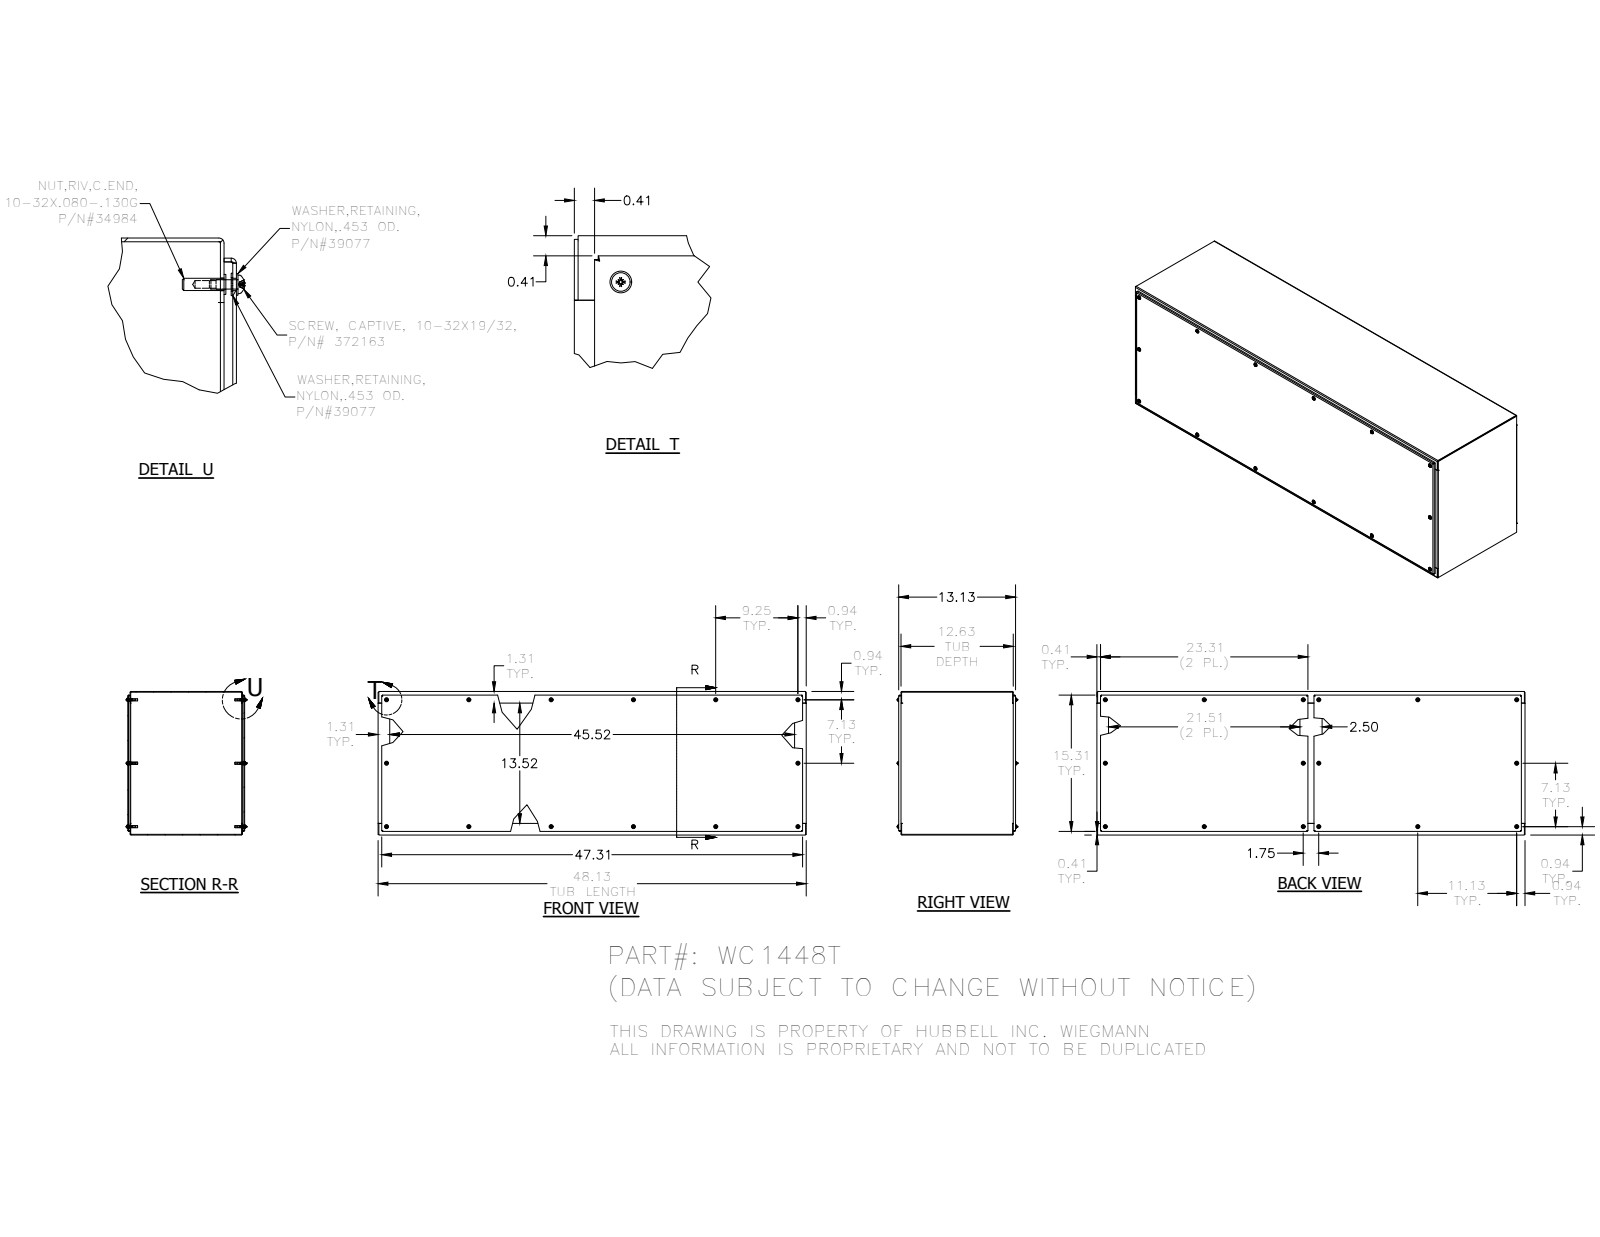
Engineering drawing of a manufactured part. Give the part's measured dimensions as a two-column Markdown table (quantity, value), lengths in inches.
| quantity | value |
| --- | --- |
| part name | 34984; WC14TLRS; WC1448TTB; 39035 (+6 more) |
| STEP written by | Autodesk Inventor 2016 (AUTOMOTIVE_DESIGN) |
| units | inches |
| bodies | 136 solids, 2638 faces (1378 planar, 550 cylindrical, 710 other) |
| overall size | 48.125 × 16.125 × 13.451 |
| volume | 255.1 in³ |
| surface area | 6 977 in² |
| round holes (diameter × count) | 0.25 × 27, 0.156 × 26, 0.196 × 26, 0.188 × 24, 0.278 × 24, 0.257 × 22, 0.179 × 4 |
| round bosses / shafts (diameter × count) | 0.406 × 26, 0.248 × 26, 0.453 × 24, 0.437 × 24, 0.373 × 24, 0.19 × 24 |
| partial cylindrical surfaces (radius × count) | 0.089 × 20, 0.031 × 18, 0.105 × 18 |
| main face-to-face distances | 0.074, 13.051, 16.051, 12.977, 13.125, 12.801, 0.25, 15.977, 16.125, 48.051 |
| hole center spacings | 14.25, 9.25, 16.989, 18.5, 18.078, 23.352, 24, 27.75 |
